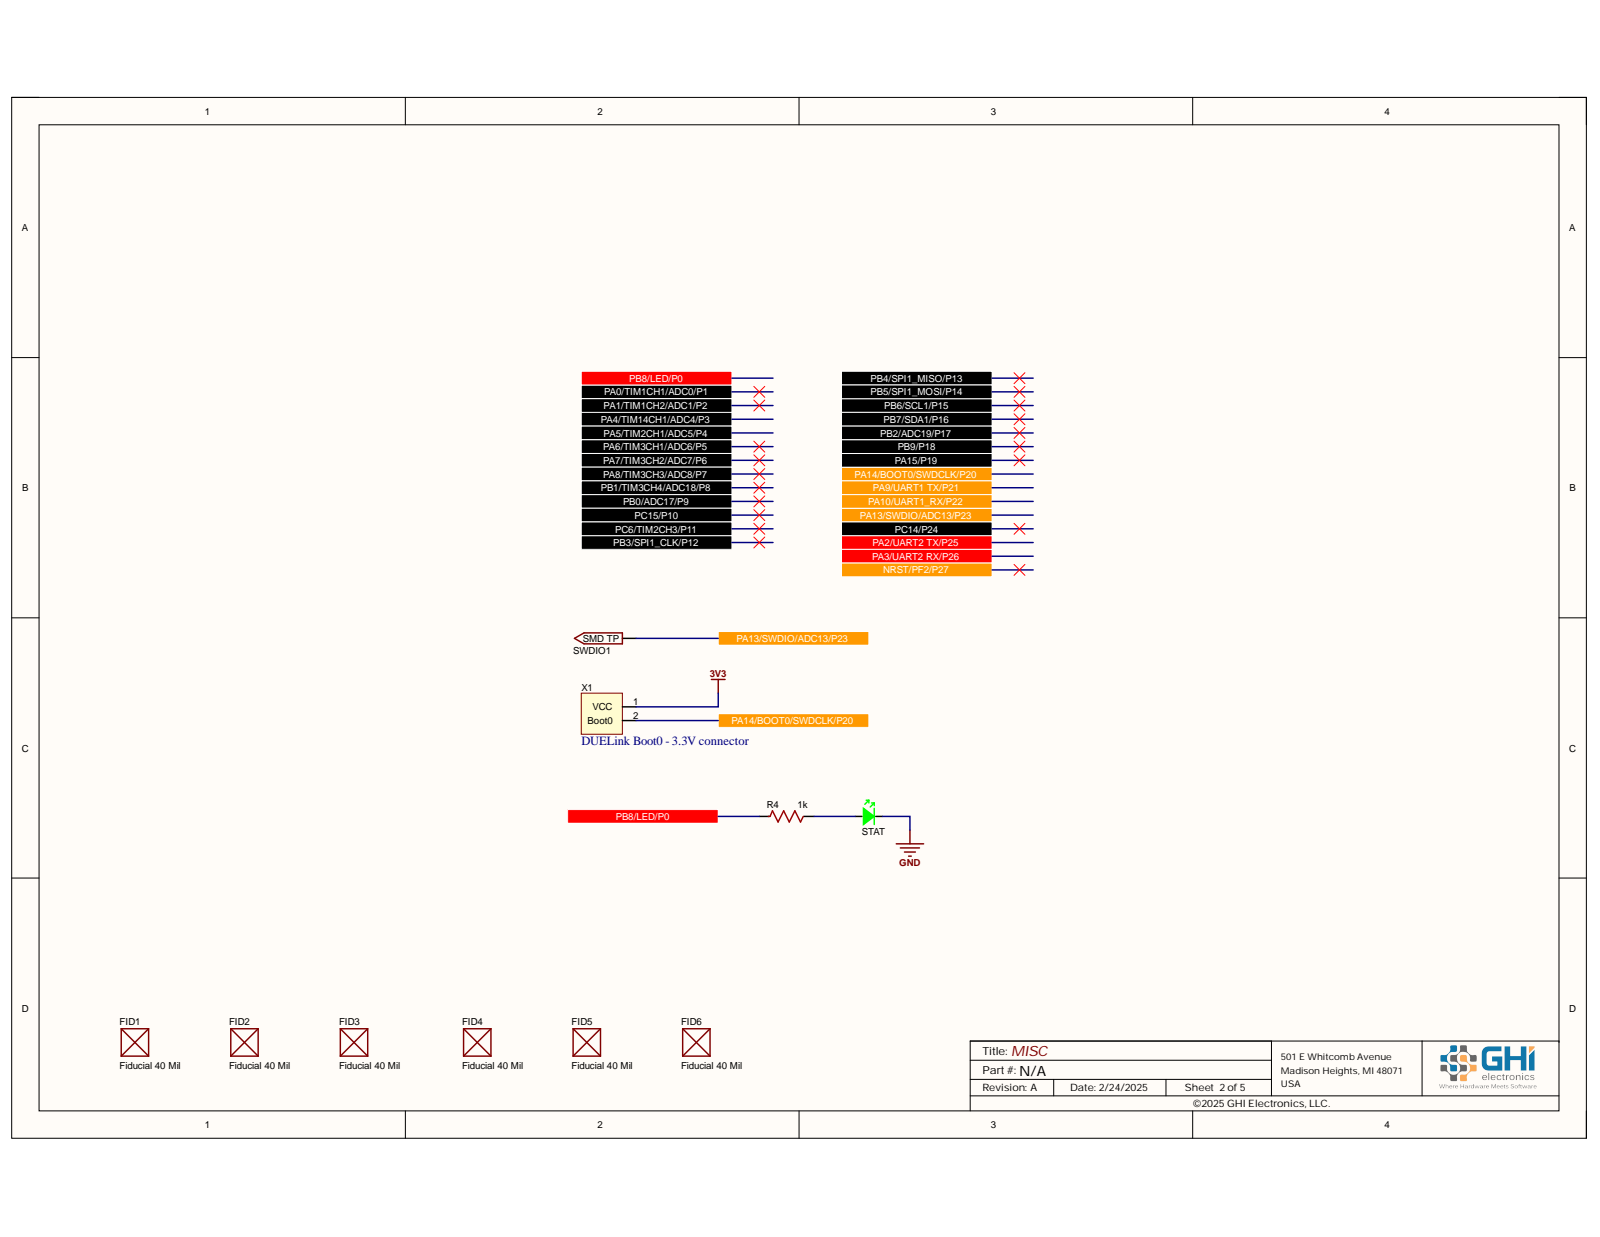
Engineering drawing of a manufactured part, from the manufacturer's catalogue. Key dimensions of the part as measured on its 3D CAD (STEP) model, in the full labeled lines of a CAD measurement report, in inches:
Part name (STEP PRODUCT): PCB; Board; U2; IC_Allegro_MicroSystems_LLC_ACS713ELCTR-30A-T_eec (+6 more)
STEP written by: Open CASCADE 7.5 (AUTOMOTIVE_DESIGN)
Units: inches
Bodies: 148 solids, 2143 faces (1538 planar, 324 cylindrical, 281 other)
Overall size (bounding box): 1.063 × 0.866 × 0.528
Volume: 0.047 in³ · Surface area: 4.825 in²
Round holes (diameter × count): ⌀0.118 ×6, ⌀0.024 ×2, ⌀0.04 ×2, ⌀0.051 ×2, ⌀0.079 ×2, ⌀0.108 ×2, ⌀0.138 ×2
Round bosses / shafts (diameter × count): ⌀0.098 ×2, ⌀0.039 ×2, ⌀0.02 ×1
Partial cylindrical surfaces — rounded edges, fillets, slot ends (radius × count): R0.005 ×37, R0.006 ×14, R0.031 ×8, R0.004 ×6, R0.008 ×4, R0.138 ×4, R0.007 ×2, R0.007 ×2
Main face-to-face distances: 0.217, 0.197, 0.157, 0.02, 0.177, 0.374, 0.039, 0.219, 0.033, 0.036
Hole centre spacings: 0.197, 0.126, 0.234, 0.28, 0.295, 0.322, 0.371, 0.492
